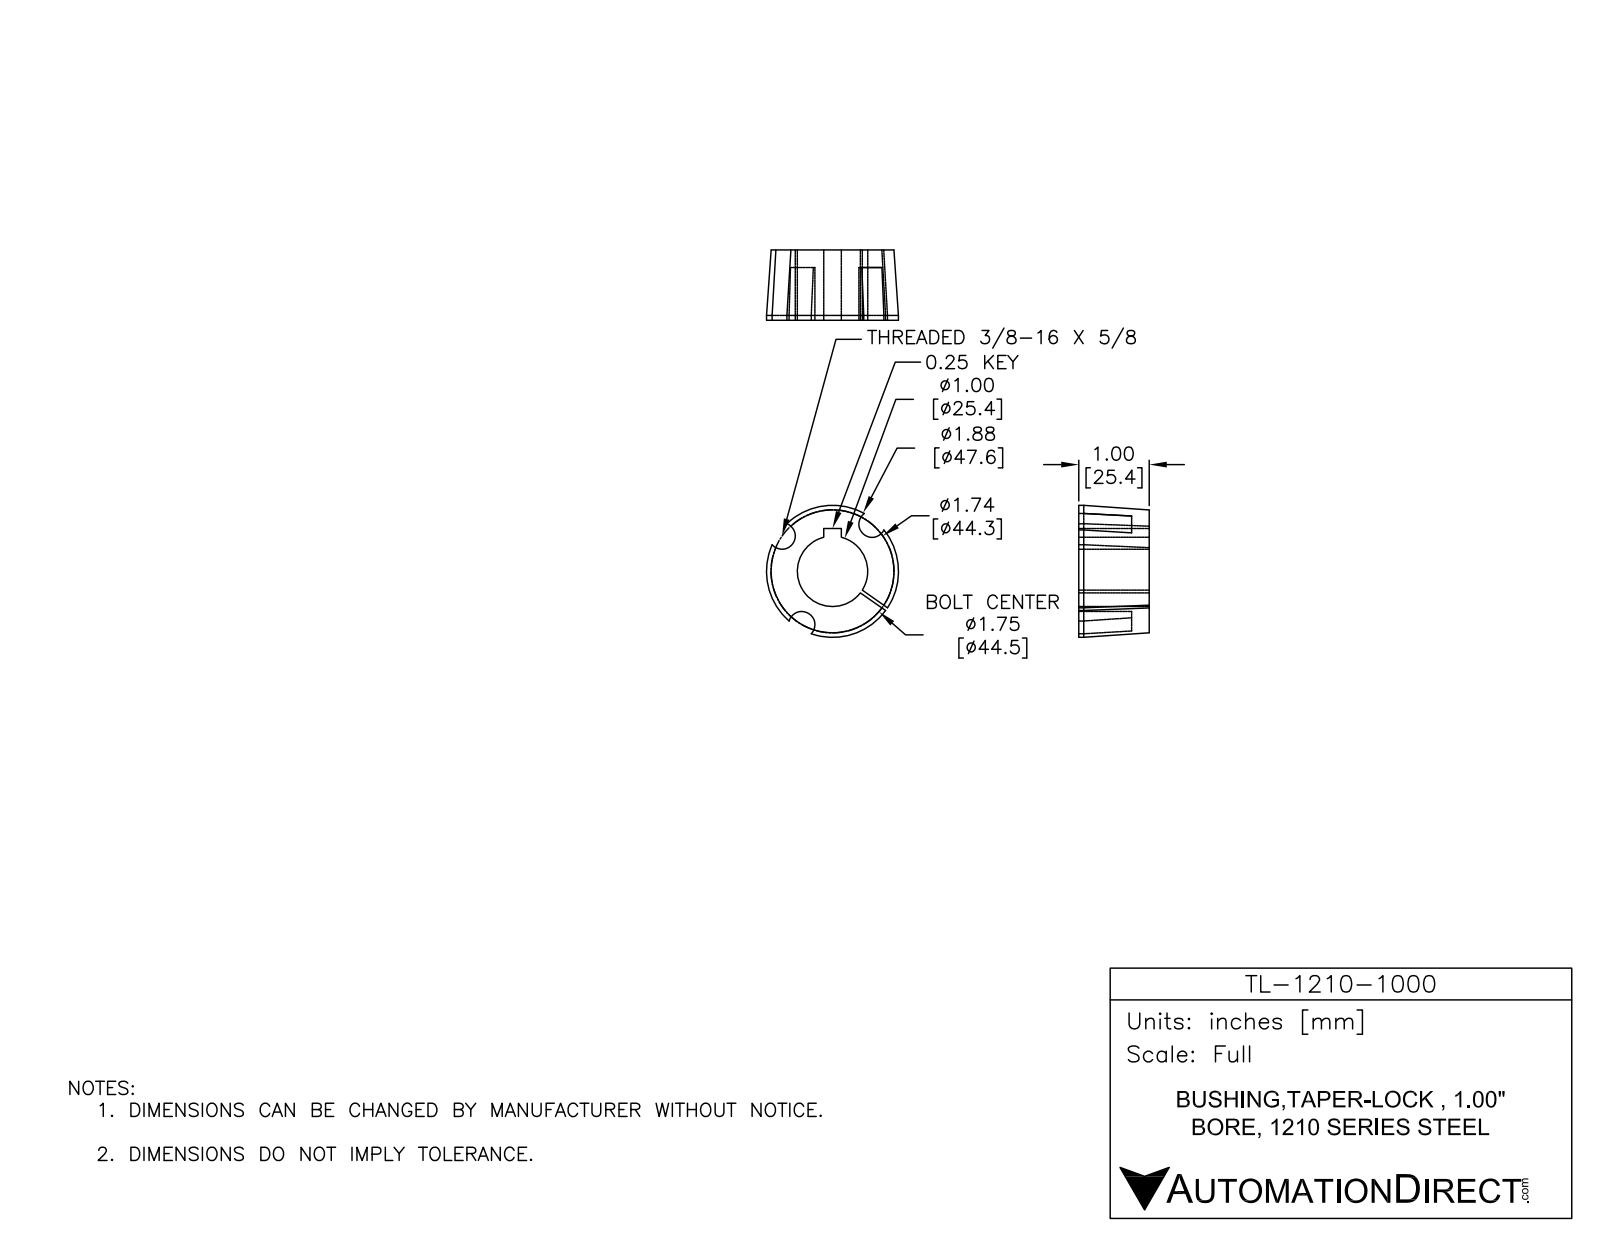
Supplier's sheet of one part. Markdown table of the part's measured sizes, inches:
| quantity | value |
| --- | --- |
| part name | TL-1210-1000 |
| STEP written by | SolidWorks 2014 (AUTOMOTIVE_DESIGN) |
| units | inches |
| bodies | 1 solid, 25 faces (9 planar, 13 cylindrical, 3 other) |
| overall size | 1.875 × 1.875 × 1 |
| volume | 1.587 in³ |
| surface area | 13.77 in² |
| round holes (diameter × count) | 1 × 1 |
| round bosses / shafts (diameter × count) | 1.875 × 1 |
| partial cylindrical surfaces (radius × count) | 0.188 × 3 |
| main face-to-face distances | 1, 0.048, 0.25, 0.25, 0.75 |
